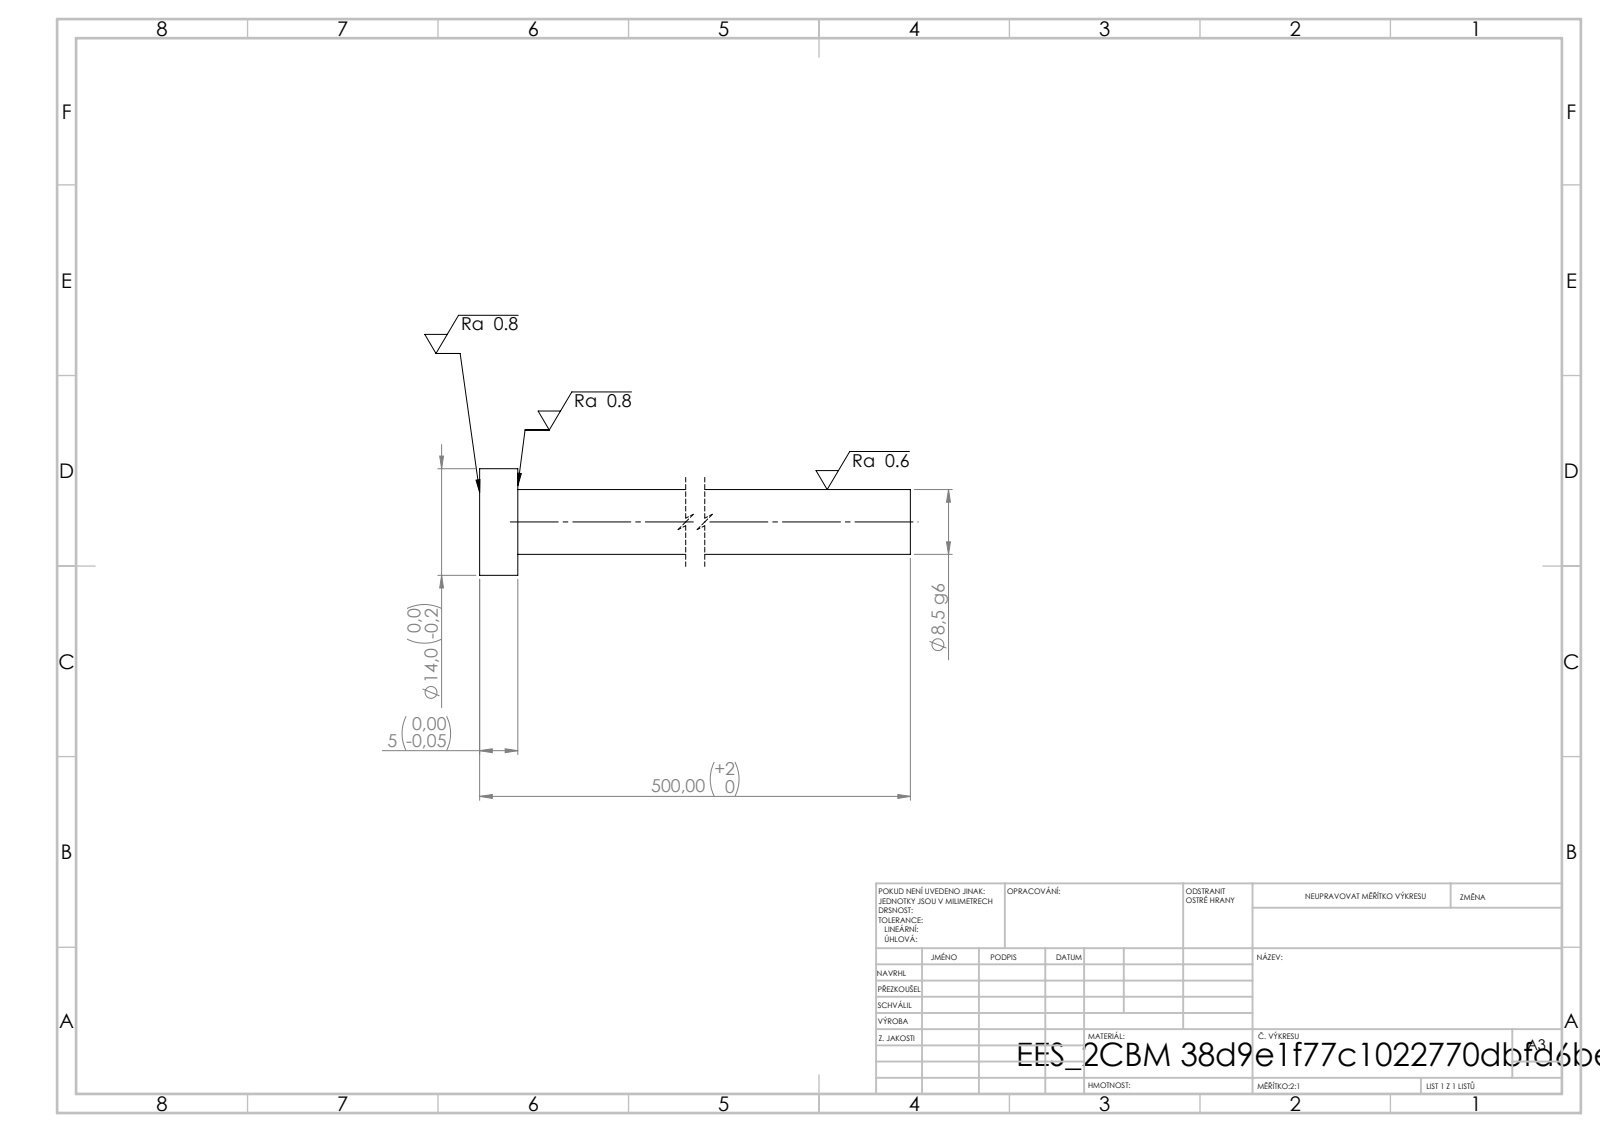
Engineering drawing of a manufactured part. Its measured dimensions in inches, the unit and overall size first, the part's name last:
Units: inches
Overall size (bounding box): 19.685 × 0.551 × 0.551
Round bosses / shafts (diameter × count): ⌀0.551 ×1, ⌀0.335 ×1
Main face-to-face distances: 0.197, 19.685, 19.488
Volume: 1.761 in³ · Surface area: 21.31 in²
Bodies: 1 solid, 7 faces (3 planar, 4 cylindrical, 0 other)
STEP written by: SolidWorks 2019 (CONFIG_CONTROL_DESIGN)
